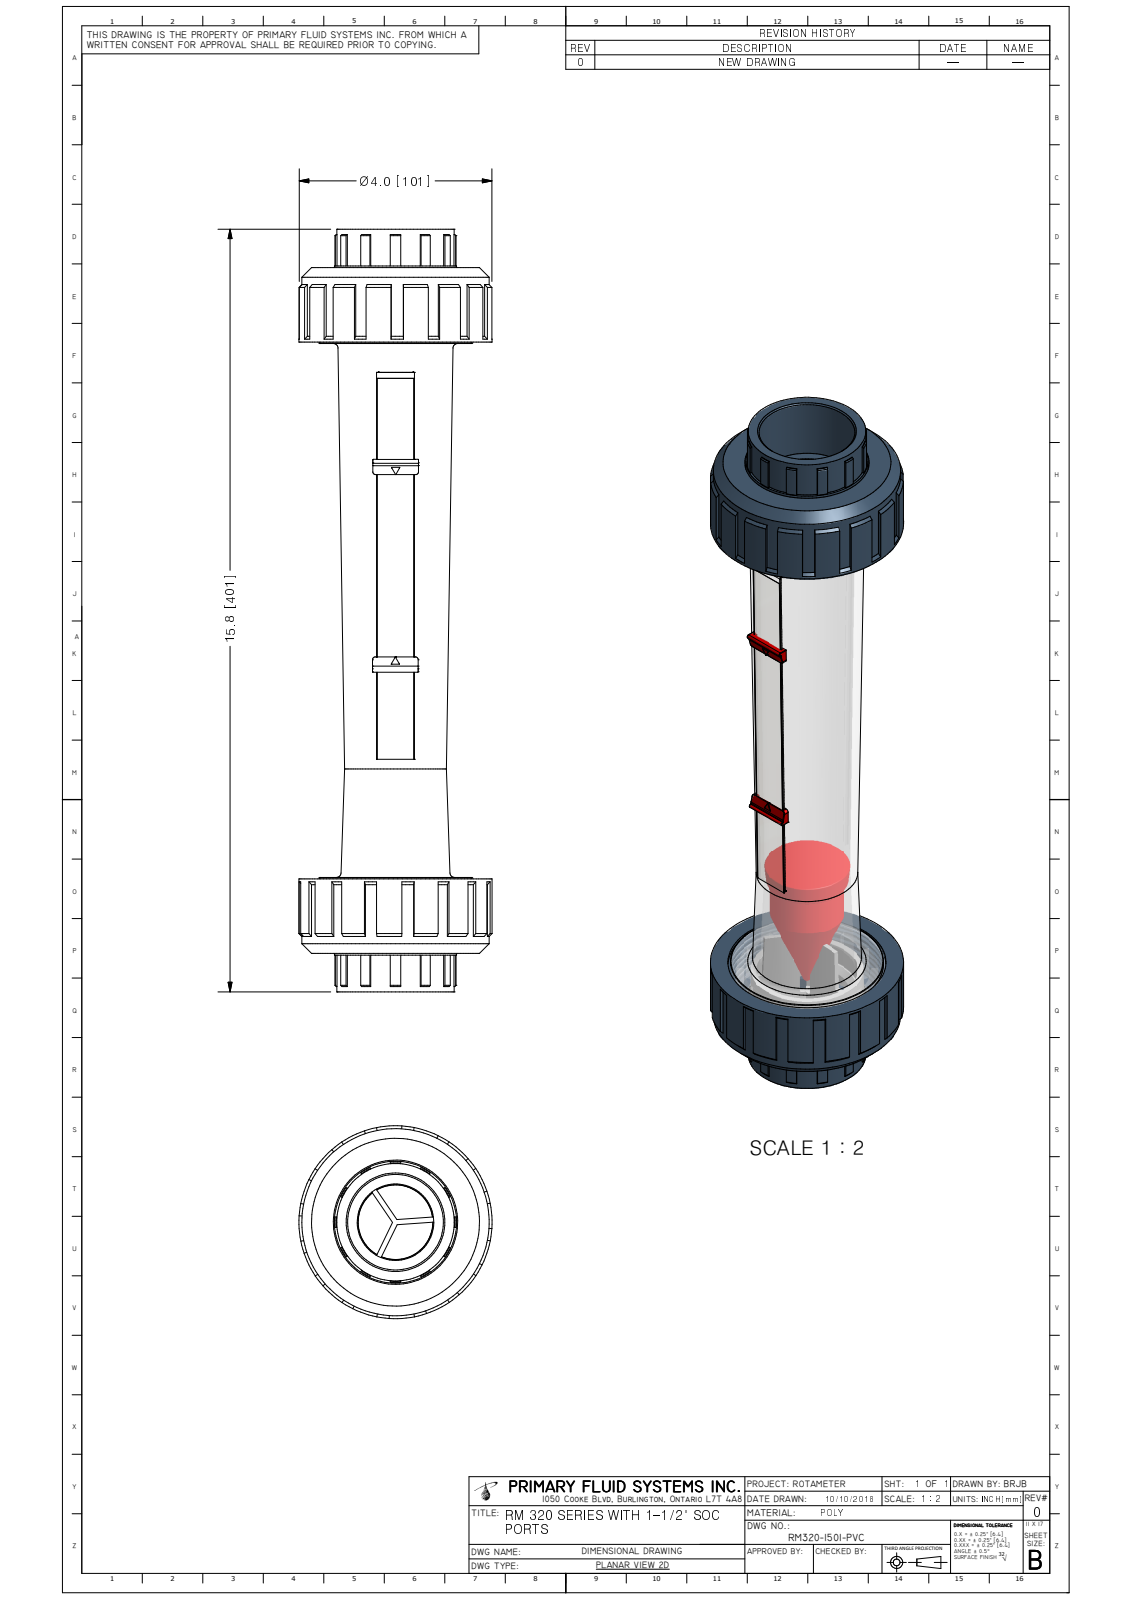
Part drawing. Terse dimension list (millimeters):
name: RM320-150I-PVC_R0
written by: Autodesk Inventor 2009 (AUTOMOTIVE_DESIGN)
unit: mm
bodies: 1 solid, 669 faces (261 planar, 132 cylindrical, 276 other)
size: 400.6 × 101.3 × 101.3
volume: 1 273 000 mm³; area: 178 300 mm²
holes: 1× ⌀50.2, 1× ⌀65.3, 1× ⌀79.9, 1× ⌀82.9, 1× ⌀82.9
bosses: 1× ⌀101.3, 1× ⌀98.3, 1× ⌀80.2, 1× ⌀76.2, 1× ⌀64.1, 1× ⌀61.7
rounds: 18× R0.2, 16× R0.3, 8× R0.1, 8× R0.2, 4× R1.5, 2× R0.2, 2× R1, 2× R19.1
face distances: 39.1, 321.1, 11.8, 348.4, 27.4, 309.3, 39.9, 320.3, 28.1, 308.5
